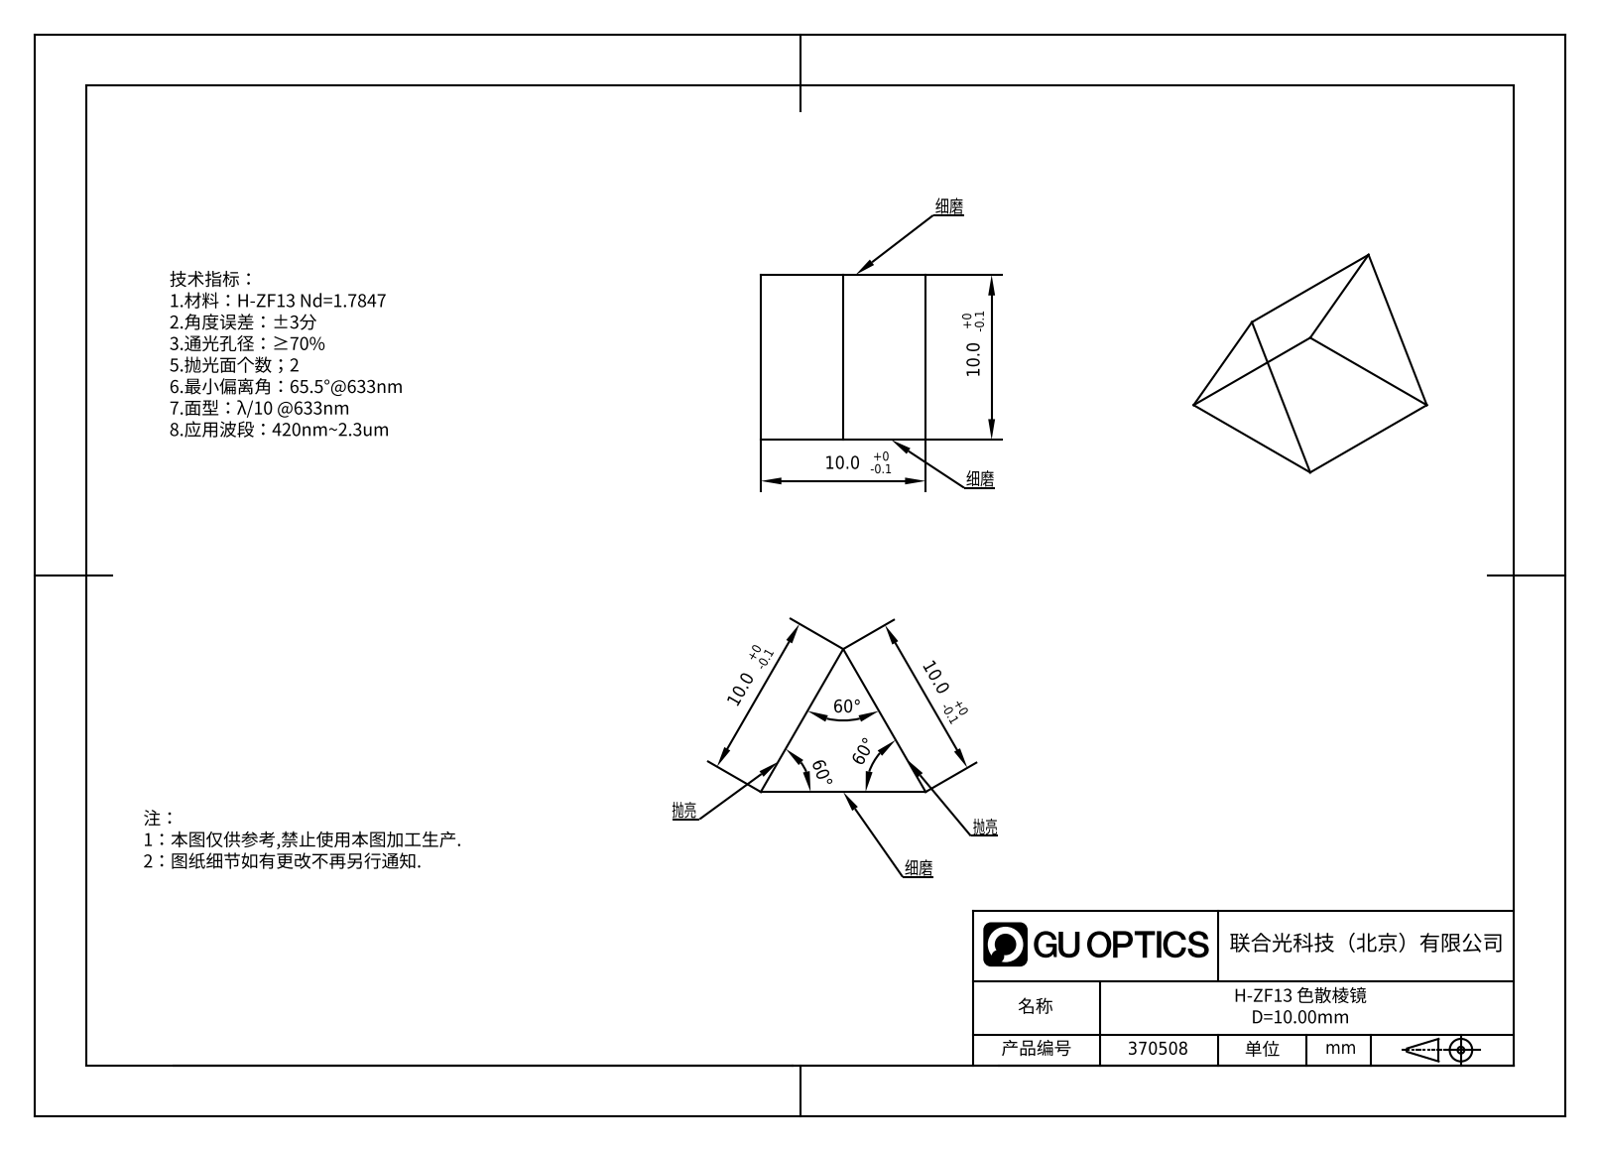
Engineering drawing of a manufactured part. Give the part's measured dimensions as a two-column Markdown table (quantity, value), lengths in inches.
| quantity | value |
| --- | --- |
| part name | GPD-010-B |
| STEP written by | SolidWorks 2022 (AUTOMOTIVE_DESIGN) |
| units | inches |
| bodies | 1 solid, 20 faces (20 planar, 0 cylindrical, 0 other) |
| overall size | 0.394 × 0.39 × 0.339 |
| volume | 0.026 in³ |
| surface area | 0.591 in² |
| main face-to-face distances | 0.394 |
